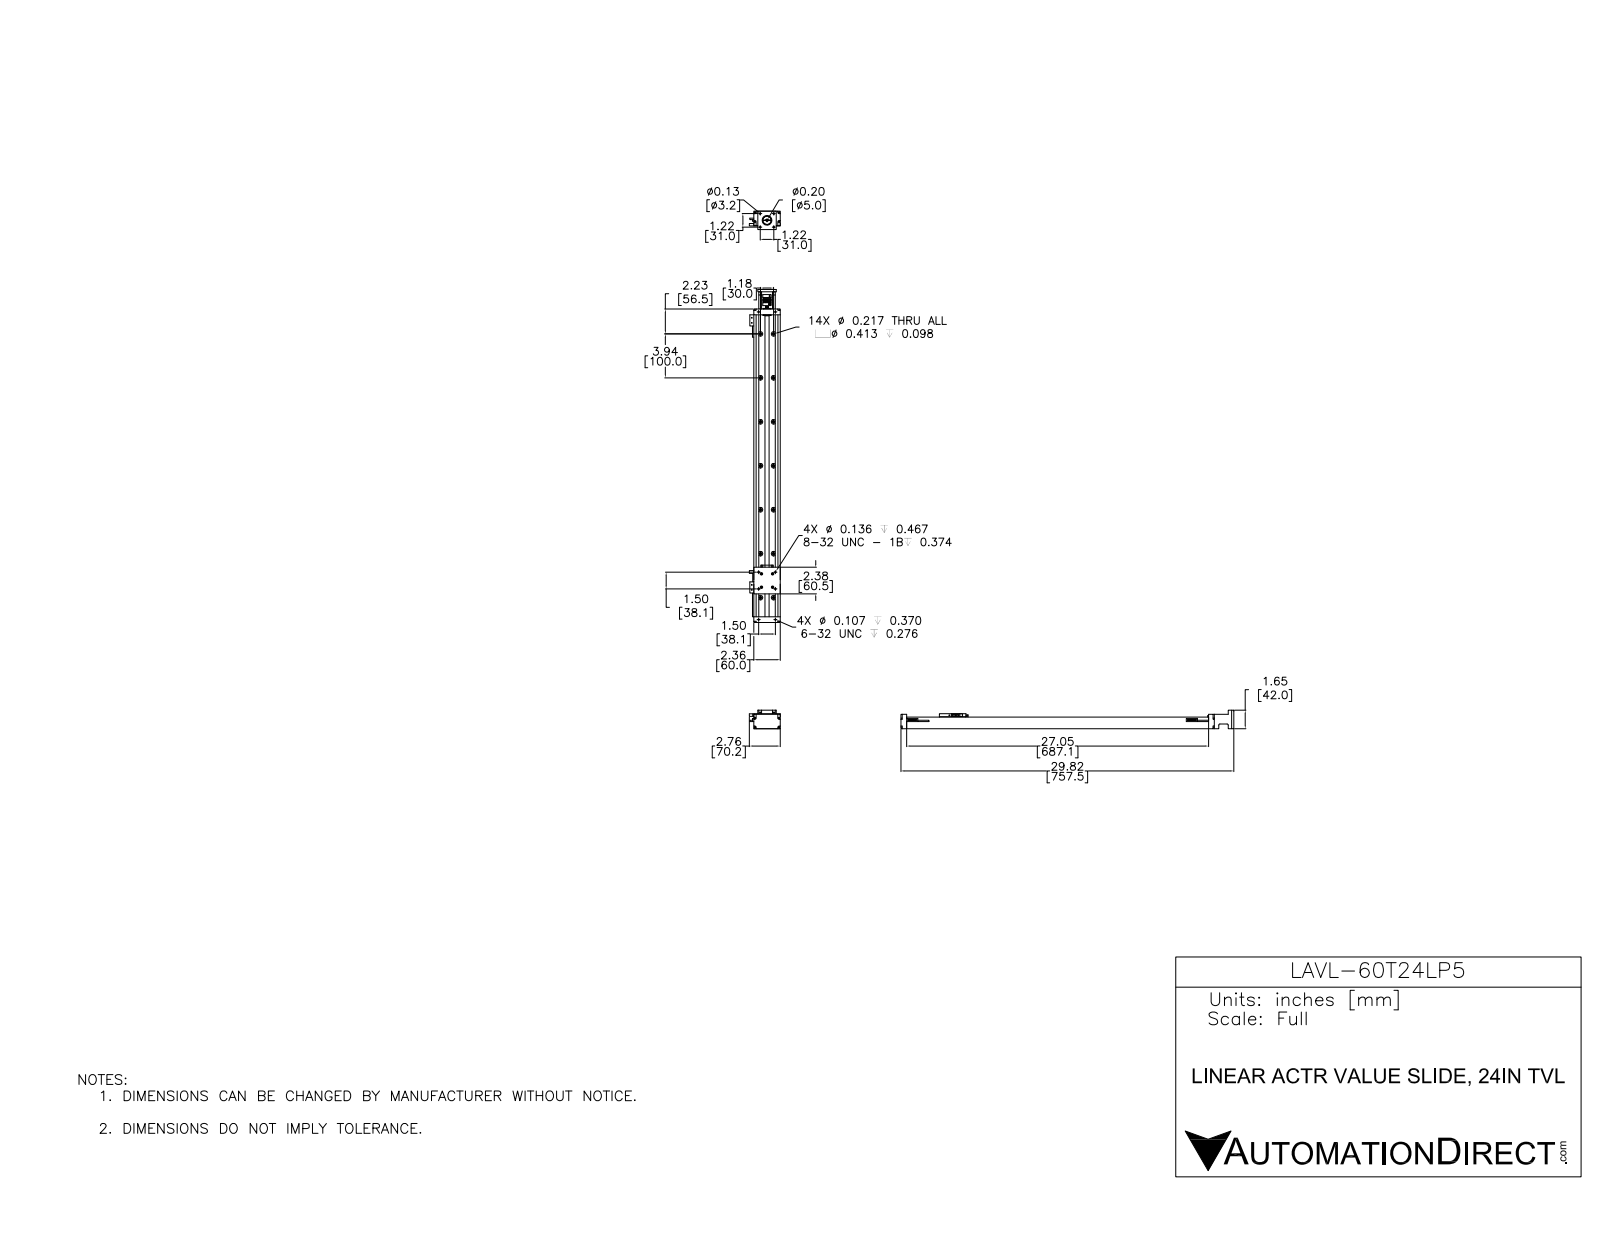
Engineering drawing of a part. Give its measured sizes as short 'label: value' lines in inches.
name: LAVL-60T24LP5; LAVL-60T06LP5-CAR; LAVL-60T24LP5-RAIL
written by: SolidWorks 2015 (AUTOMOTIVE_DESIGN)
unit: in
bodies: 19 solids, 888 faces (336 planar, 383 cylindrical, 169 other)
size: 29.824 × 2.762 × 1.654
volume: 37.23 in³; area: 445 in²
holes: 14× ⌀0.217, 14× ⌀0.413, 12× ⌀0.129, 10× ⌀0.107, 6× ⌀0.089, 6× ⌀0.136, 4× ⌀0.086, 4× ⌀0.12, 4× ⌀0.125, 4× ⌀0.125, 4× ⌀0.15, 4× ⌀0.219
bosses: 4× ⌀0.22, 4× ⌀0.209, 2× ⌀0.157, 1× ⌀0.748, 1× ⌀0.69, 1× ⌀0.673, 1× ⌀0.625, 1× ⌀0.508
rounds: 8× R0.109, 4× R0.047, 4× R0.211, 4× R0.266, 3× R0.047, 3× R0.188, 2× R0.057, 2× R0.062
face distances: 0.2, 2.162, 2.362, 1.962, 0.445, 0.645, 1.044, 0.844, 0.399, 0.555
hole spacings: 2.162, 3.937, 4.11, 1.089, 2.316, 7.874, 7.962, 1.181
